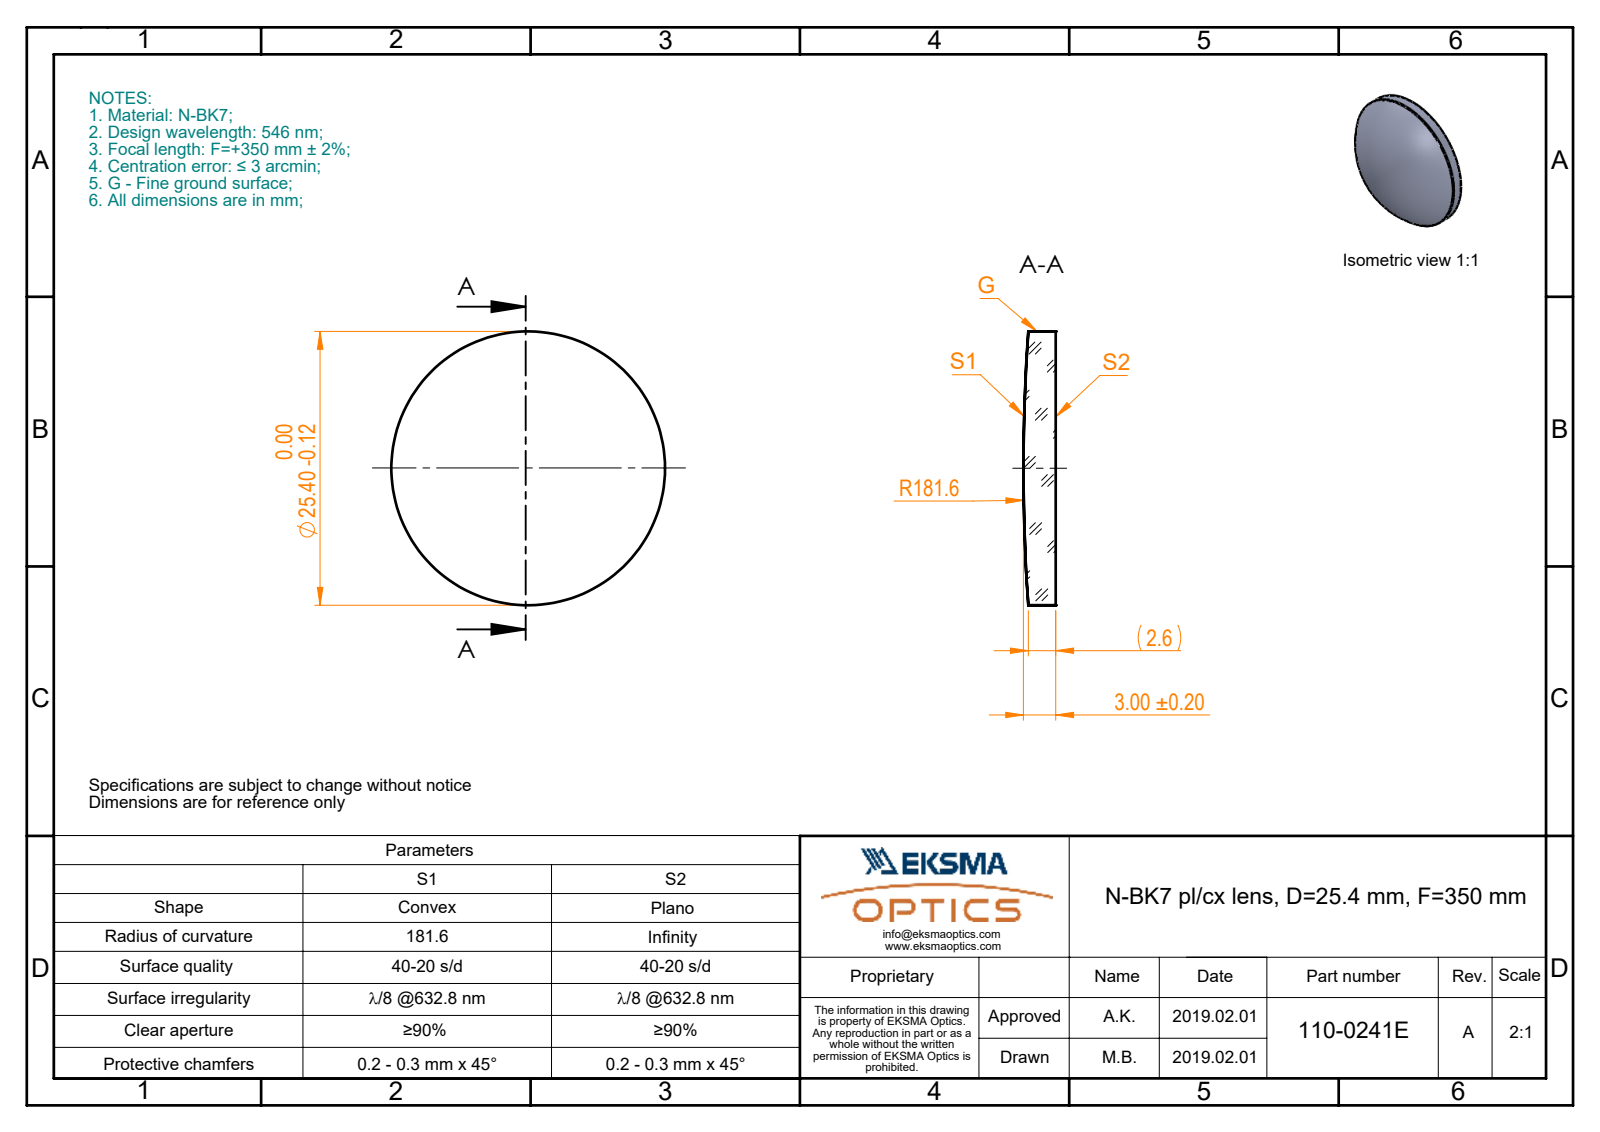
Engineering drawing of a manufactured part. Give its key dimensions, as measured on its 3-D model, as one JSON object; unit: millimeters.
{"part_name": "110-0241E BK7 pl-cx 25.4 F350", "step_written_by": "SolidWorks 2017 (CONFIG_CONTROL_DESIGN)", "units": "millimeters", "bodies": {"solids": 1, "faces": 5, "planar": 1, "cylindrical": 2, "other": 2}, "overall_size": [25.4, 25.4, 3], "volume_mm3": 1408, "surface_area_mm2": 1218, "round_bosses_or_shafts": [[25.4, 1]]}
